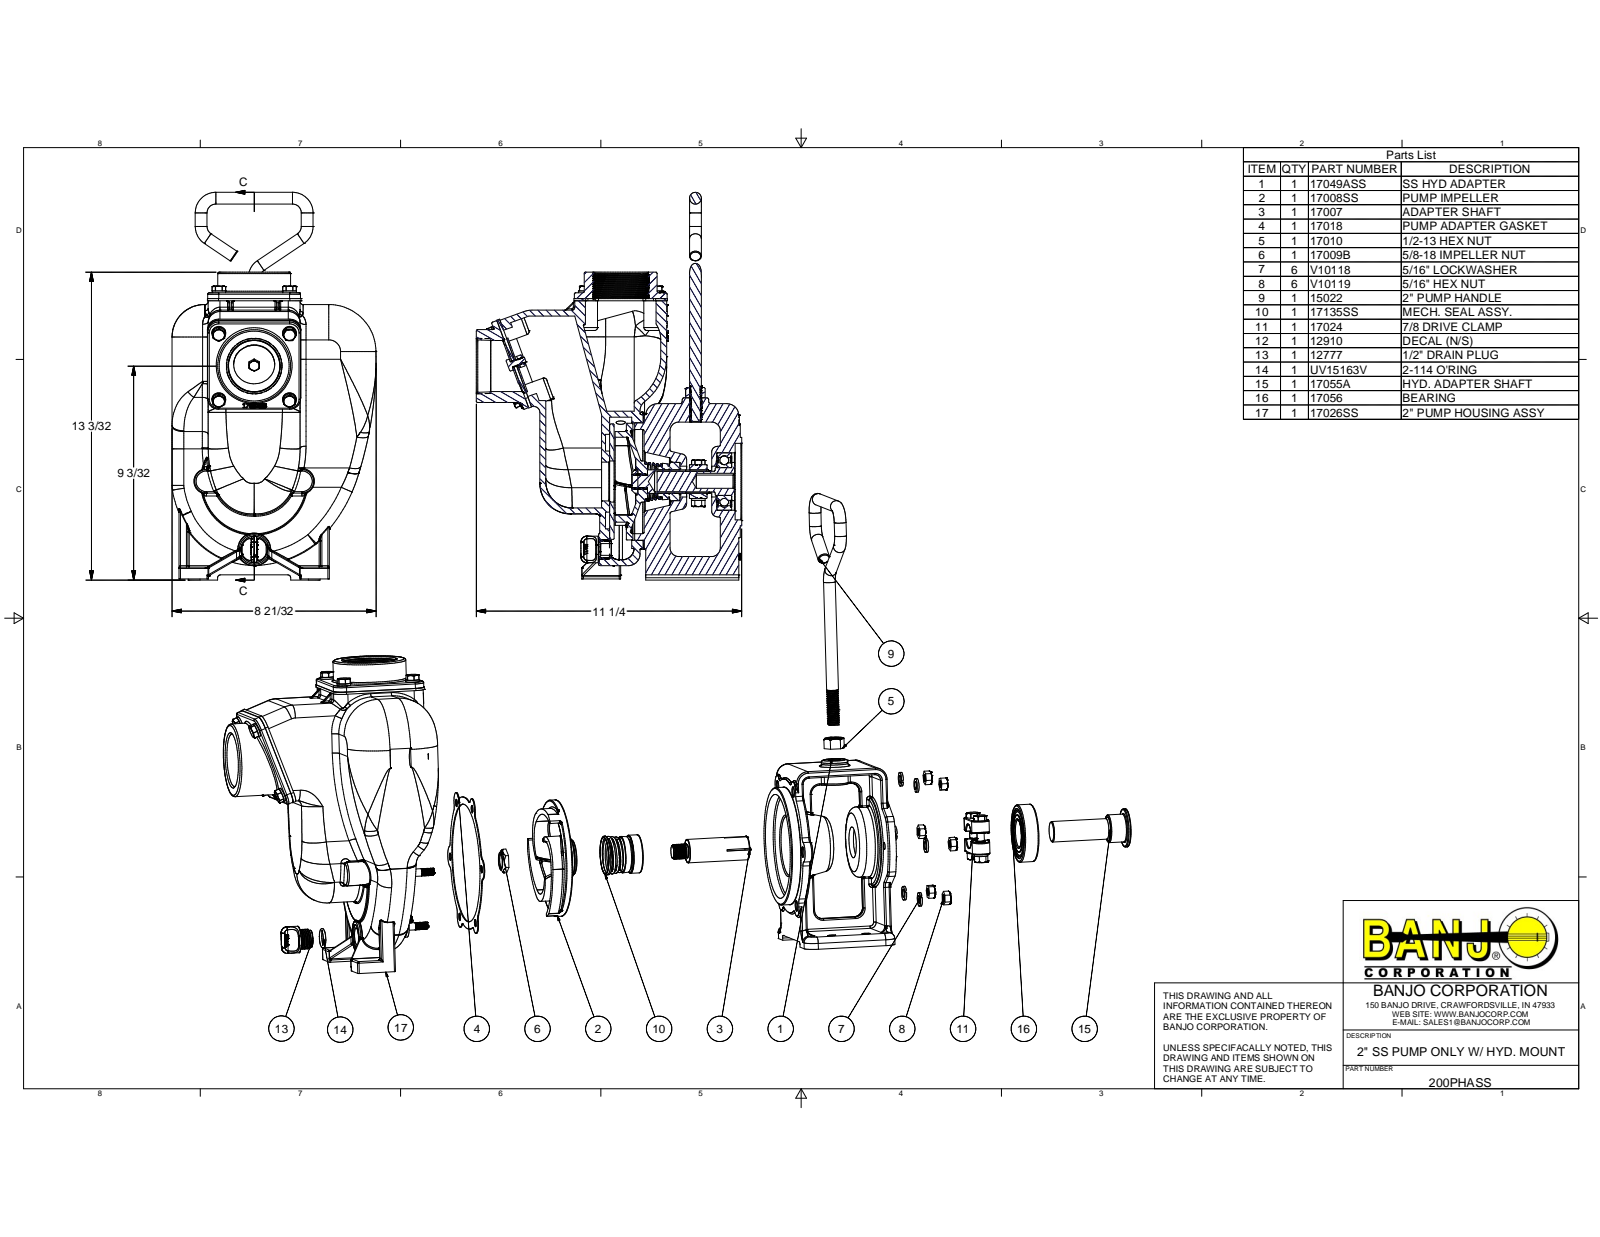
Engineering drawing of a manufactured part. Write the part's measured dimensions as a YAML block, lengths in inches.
part_name: "200PHASS; 17026SS; 17026SSX; 17000SS (+8 more)"
step_written_by: "Autodesk Inventor 2013 (AUTOMOTIVE_DESIGN)"
units: inches
bodies: {solids: 85, faces: 5614, planar: 1230, cylindrical: 1729, other: 2655}
overall_size: [16.479, 11.262, 8.658]
volume: 167.4
surface_area: 1373
round_holes:
  - {diameter: 0.252, count: 17}
  - {diameter: 0.322, count: 16}
  - {diameter: 0.252, count: 8}
  - {diameter: 0.313, count: 8}
  - {diameter: 0.343, count: 8}
  - {diameter: 0.38, count: 6}
  - {diameter: 0.34, count: 4}
  - {diameter: 0.187, count: 3}
  - {diameter: 0.307, count: 2}
  - {diameter: 0.35, count: 2}
  - {diameter: 0.5, count: 2}
  - {diameter: 0.196, count: 1}
round_bosses_or_shafts:
  - {diameter: 0.268, count: 162}
  - {diameter: 0.583, count: 16}
  - {diameter: 0.313, count: 12}
  - {diameter: 0.212, count: 12}
  - {diameter: 0.246, count: 6}
  - {diameter: 0.5, count: 5}
  - {diameter: 3.094, count: 2}
  - {diameter: 5.69, count: 1}
partial_cylinders:
  - {radius: 0.06, count: 78}
  - {radius: 0.25, count: 59}
  - {radius: 0.03, count: 52}
  - {radius: 0.125, count: 31}
  - {radius: 0.5, count: 29}
  - {radius: 0.063, count: 20}
  - {radius: 0.438, count: 20}
  - {radius: 0.09, count: 18}
face_to_face_distances: [0.25, 0.281, 0.125, 3.65, 0.28, 1.464, 1.815, 0.351, 0.063, 0.337]
hole_center_spacings: [3, 2.121, 2.813, 4.243, 4.242, 4.243, 4.872, 2.122]
